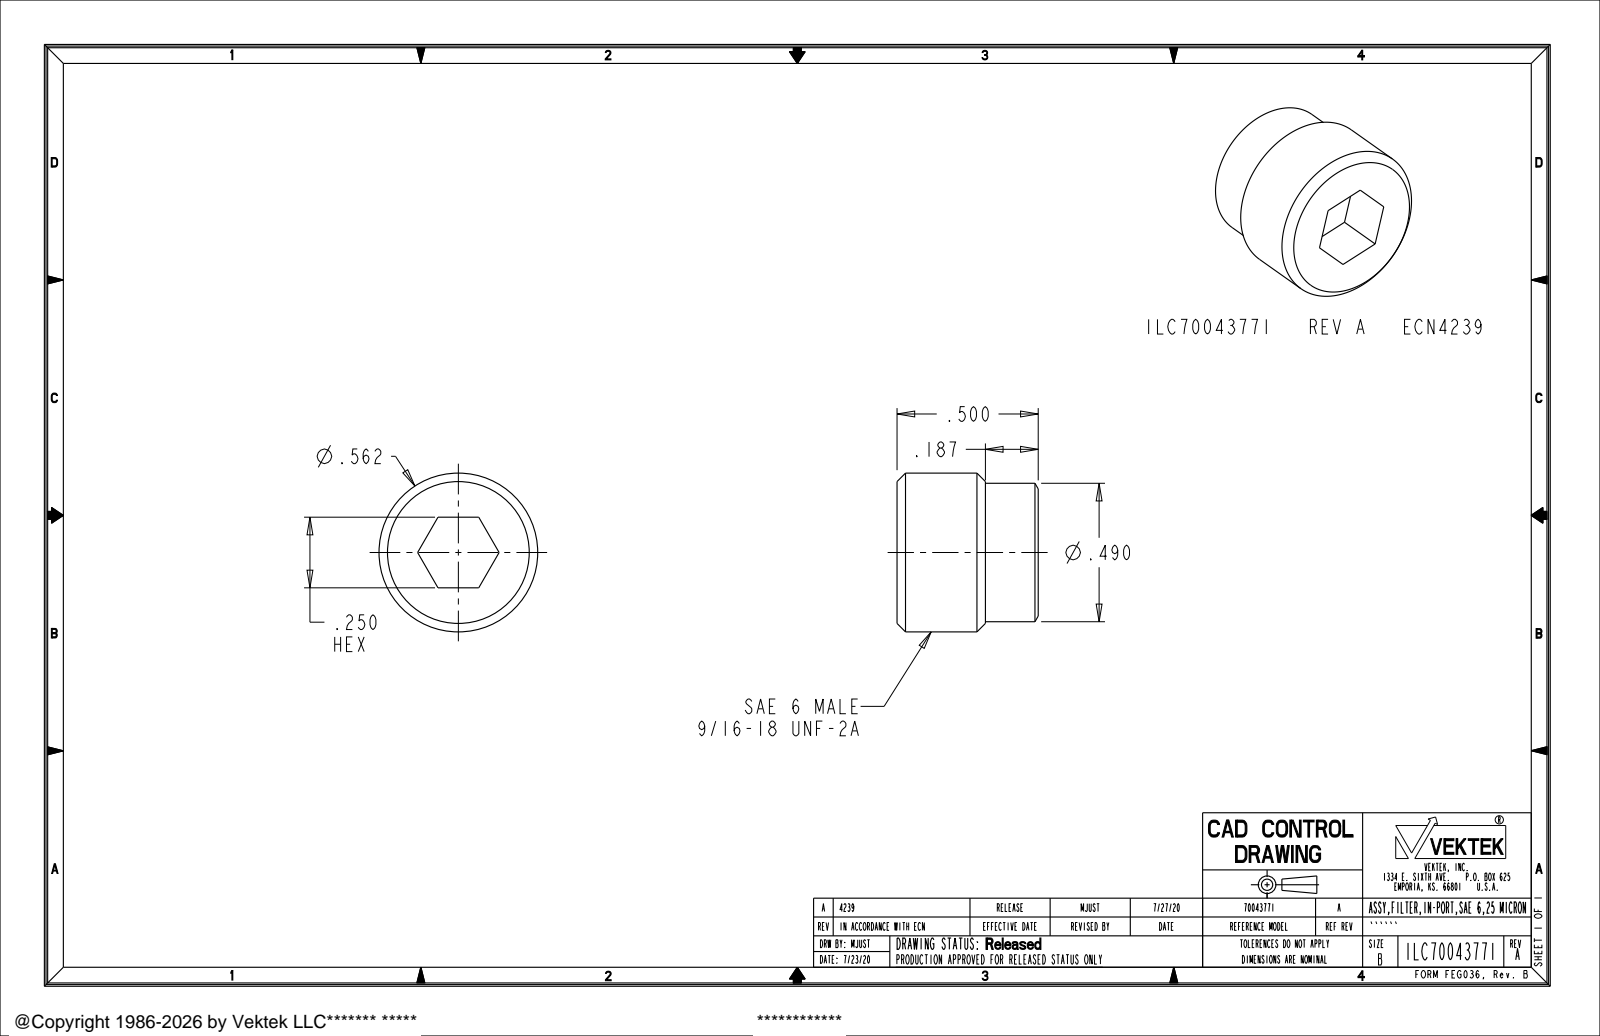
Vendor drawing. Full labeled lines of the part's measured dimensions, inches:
Part name (STEP PRODUCT): ILC70043771
STEP written by: PRO/ENGINEER BY PARAMETRIC TECHNOLOGY CORPORATION, 2017170 (AUTOMOTIVE_DESIGN)
Units: inches
Bodies: 1 solid, 23 faces (11 planar, 6 cylindrical, 6 other)
Overall size (bounding box): 0.562 × 0.562 × 0.5
Volume: 0.086 in³ · Surface area: 1.572 in²
Round holes (diameter × count): ⌀0.392 ×1
Round bosses / shafts (diameter × count): ⌀0.562 ×1, ⌀0.49 ×1
Main face-to-face distances: 0.378, 0.25, 0.19, 0.188, 0.122, 0.312, 0.5, 0.187, 0.065, 0.125
